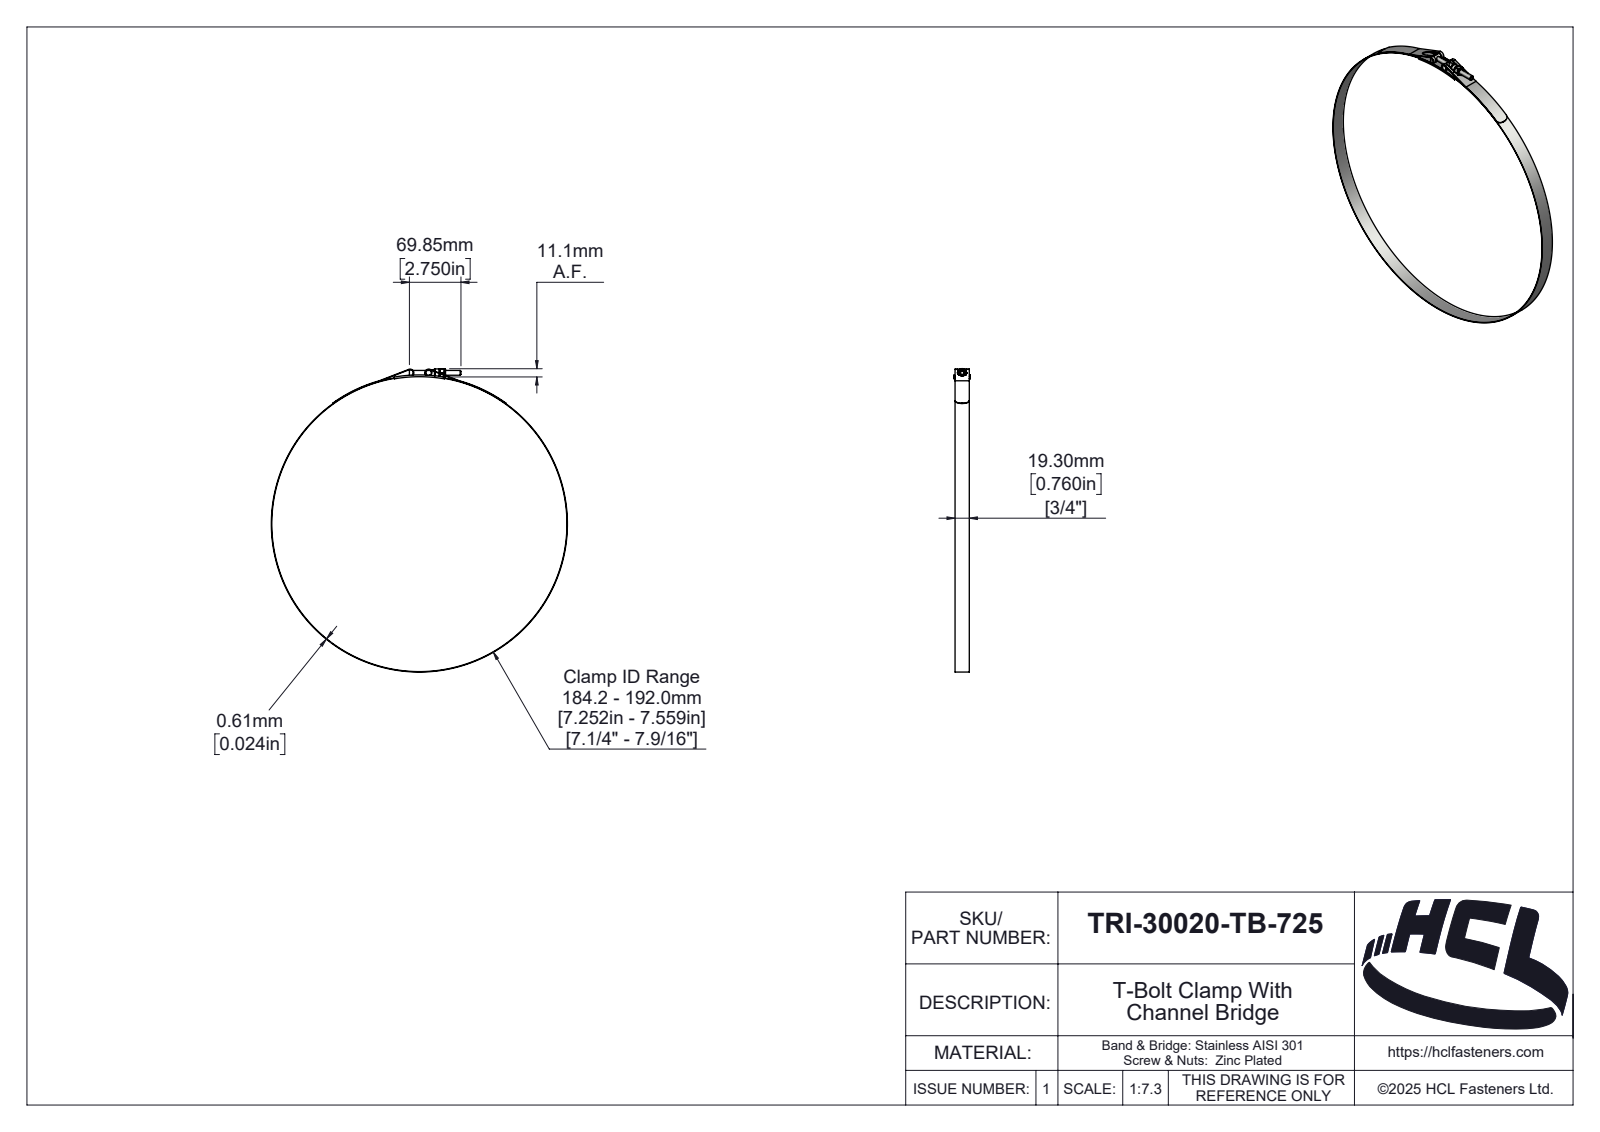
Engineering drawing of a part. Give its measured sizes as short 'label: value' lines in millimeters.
name: TRI-30020-TB-725
written by: SolidWorks 2025 (AUTOMOTIVE_DESIGN)
unit: mm
bodies: 6 solids, 330 faces (44 planar, 122 cylindrical, 164 other)
size: 410.95 × 401.22 × 22
volume: 22 315 mm³; area: 65 847 mm²
holes: 1× ⌀5.4, 1× ⌀6.35, 1× ⌀6.5, 1× ⌀7.58, 1× ⌀400
bosses: 2× ⌀8.58, 1× ⌀401.22, 1× ⌀10.58
rounds: 6× R0.39, 2× R0.5, 2× R4.39, 2× R5, 1× R0.59, 1× R2.42, 1× R3.03, 1× R3.19
face distances: 0.61, 19.3, 1.35, 20.65, 0.74, 21.39, 20.04, 22, 20.78, 41
hole spacings: 205
